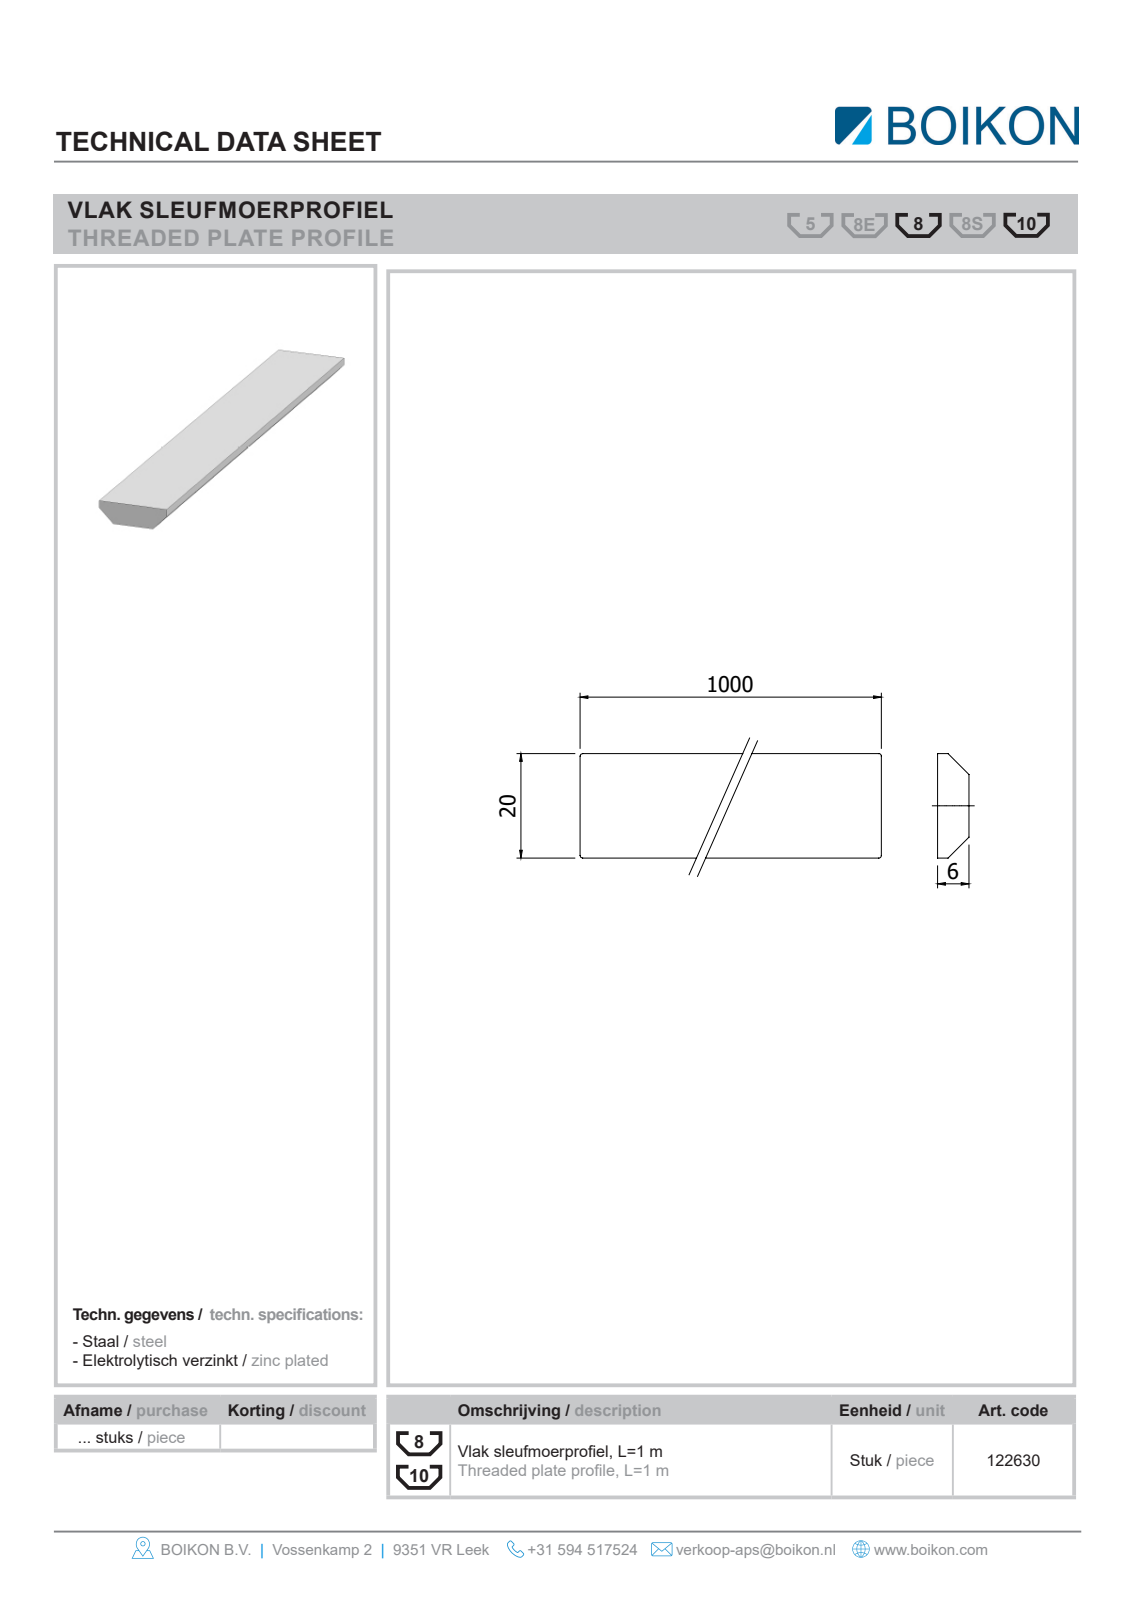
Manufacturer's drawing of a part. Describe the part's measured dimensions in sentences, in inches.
The part is named "Root; 122630Sleufmoerprofiel vlak 10 L= 1mBOIKON0". Its 3-D file was written by "HiCAD 2013 1802.4 Build 509 (AUTOMOTIVE_DESIGN)". It is 1 solid with 8 faces: 8 planar, 0 cylindrical and 0 other. Overall it measures 39.37 by 0.768 by 0.236 inches. Its volume is 6.163 cubic inches and its surface area 72.1 square inches. The main face-to-face distances are 0.236, 0.768, 39.37.
